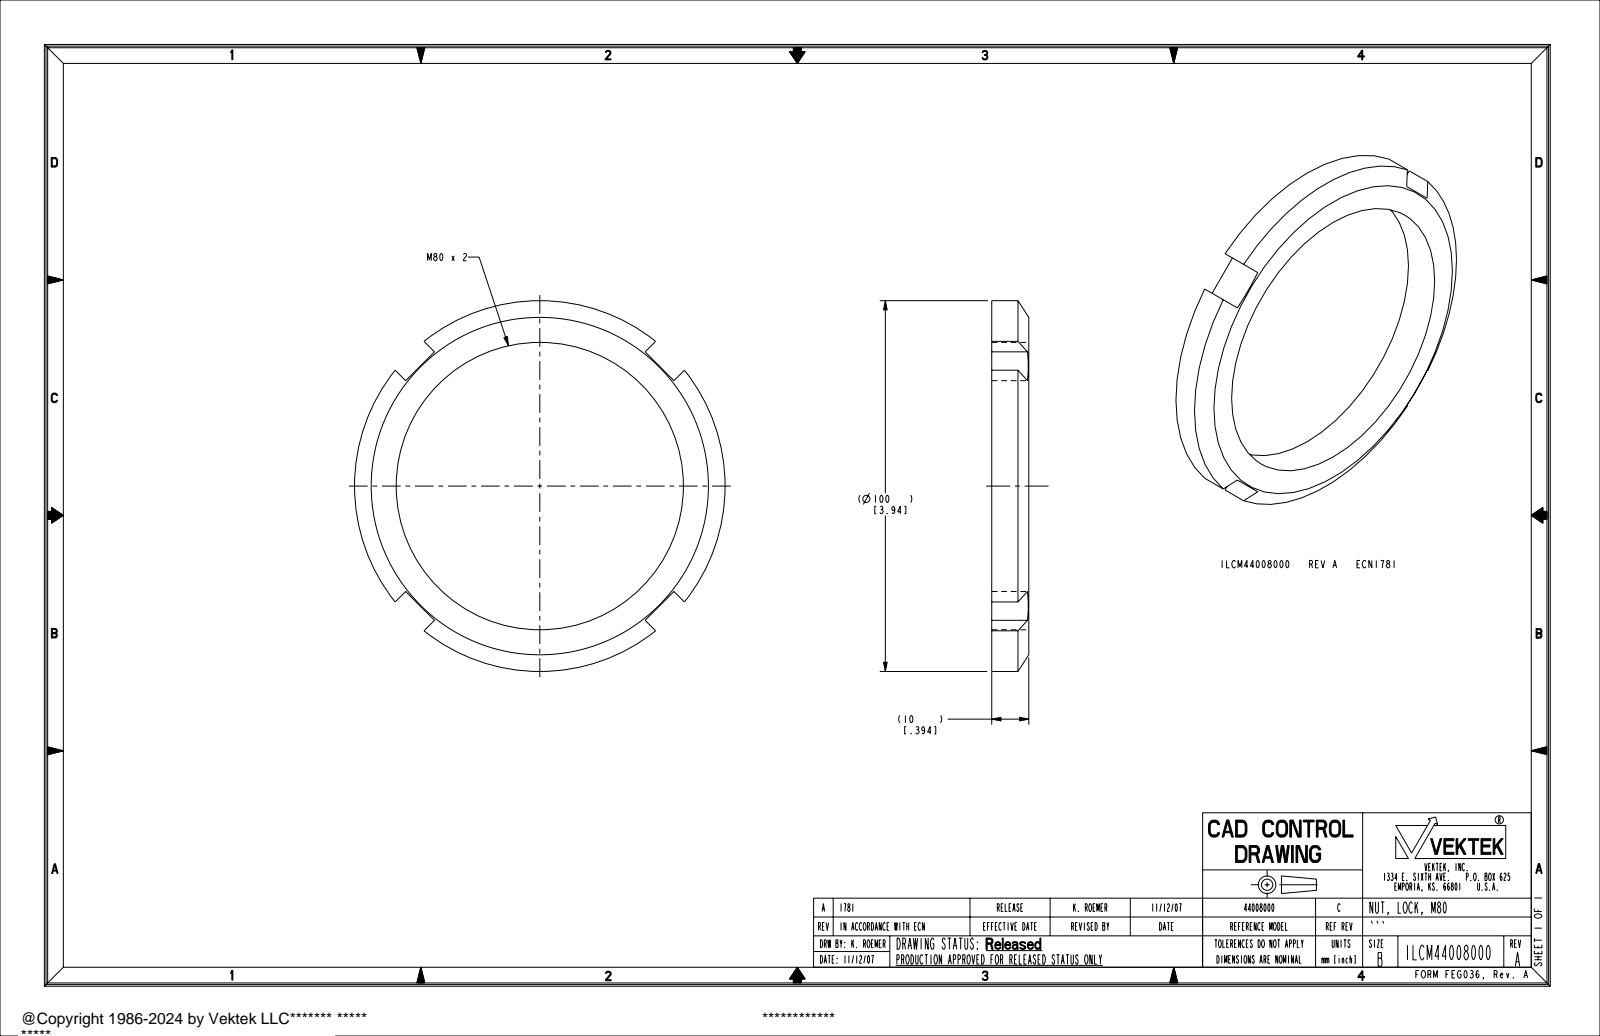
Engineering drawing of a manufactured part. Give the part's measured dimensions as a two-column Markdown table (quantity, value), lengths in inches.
| quantity | value |
| --- | --- |
| part name | ILCM44008000 |
| STEP written by | PRO/ENGINEER BY PARAMETRIC TECHNOLOGY CORPORATION, 2005180 (AUTOMOTIVE_DESIGN_CC2) |
| units | inches |
| bodies | 1 solid, 22 faces (14 planar, 6 cylindrical, 2 other) |
| overall size | 3.937 × 3.937 × 0.394 |
| volume | 1.697 in³ |
| surface area | 17.32 in² |
| round holes (diameter × count) | 3.051 × 1 |
| round bosses / shafts (diameter × count) | 3.937 × 1 |
| main face-to-face distances | 0.394, 1.582, 2.015, 3.598, 0.433 |
